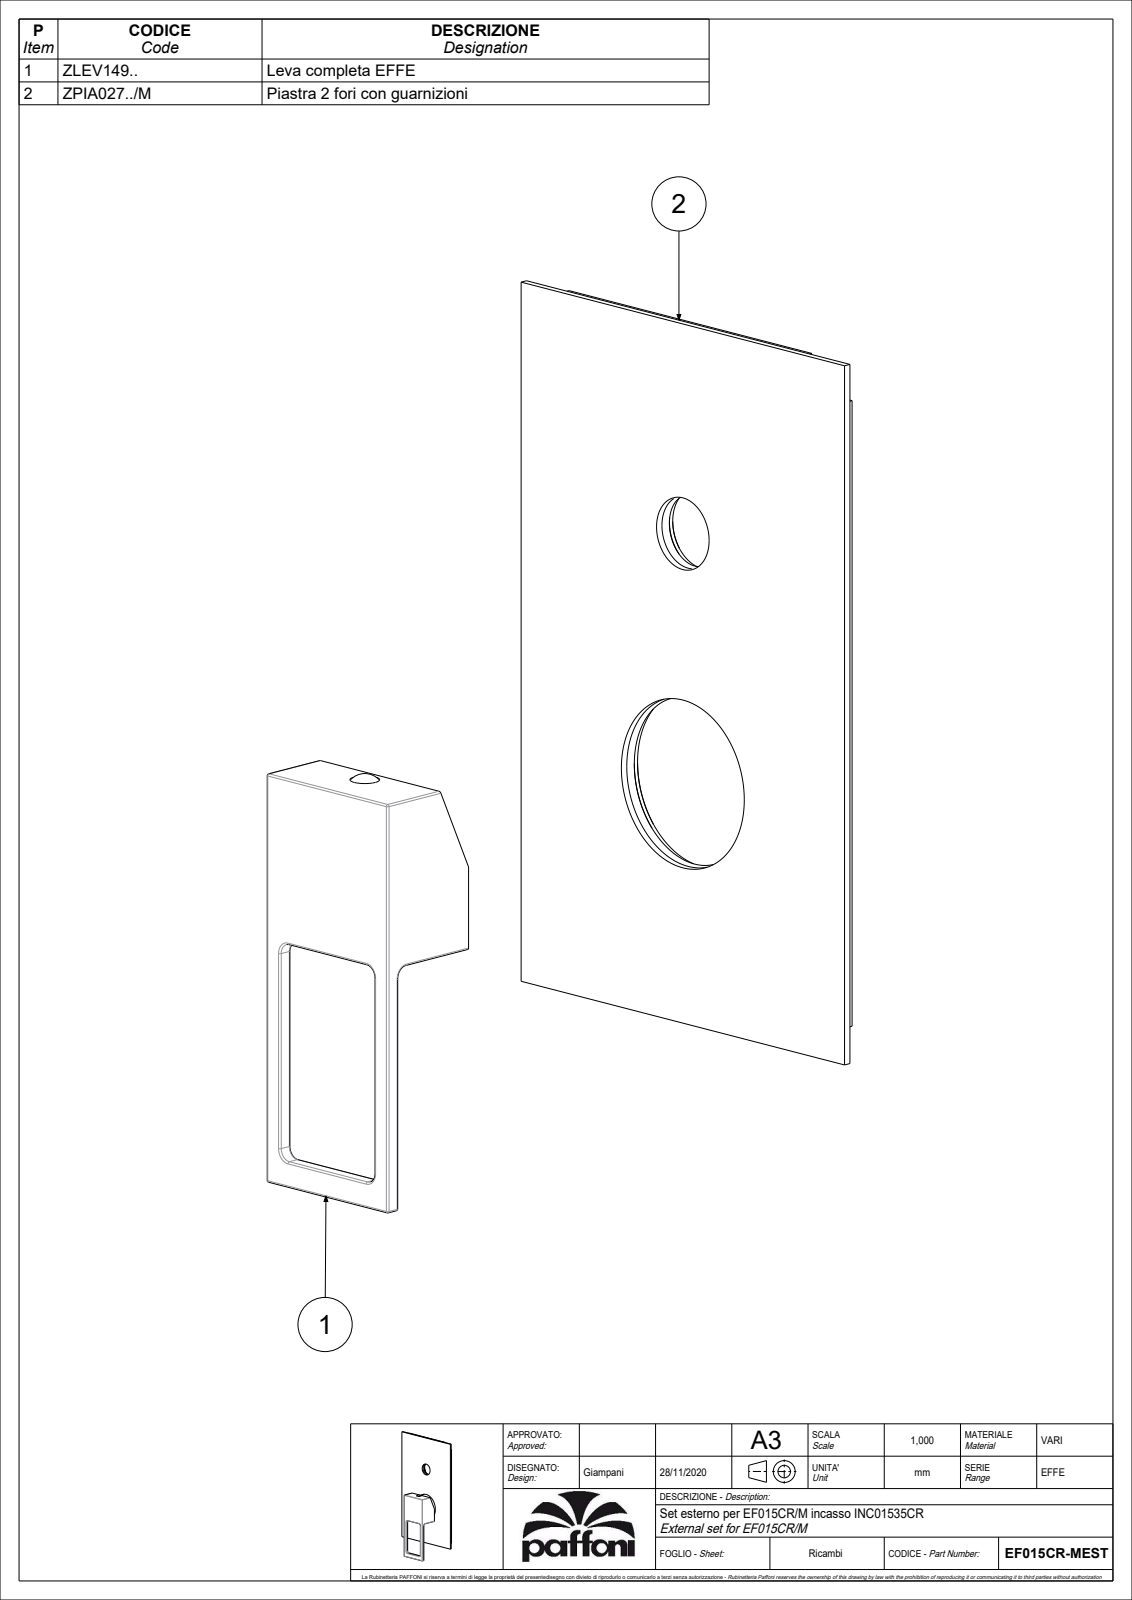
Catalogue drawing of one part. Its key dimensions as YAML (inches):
part_name: "EF015CR-MEST"
step_written_by: "CREO PARAMETRIC BY PTC INC, 2020044 (CONFIG_CONTROL_DESIGN)"
units: inches
bodies: {solids: 2, faces: 182, planar: 81, cylindrical: 67, other: 34}
overall_size: [8.366, 4.724, 1.555]
volume: 4.109
surface_area: 102.4
round_holes:
  - {diameter: 0.118, count: 1}
  - {diameter: 0.177, count: 1}
  - {diameter: 0.217, count: 1}
  - {diameter: 0.307, count: 1}
  - {diameter: 0.768, count: 1}
  - {diameter: 0.846, count: 1}
  - {diameter: 0.984, count: 1}
  - {diameter: 1.795, count: 1}
  - {diameter: 1.874, count: 1}
  - {diameter: 2.012, count: 1}
round_bosses_or_shafts:
  - {diameter: 2.15, count: 1}
  - {diameter: 1.122, count: 1}
  - {diameter: 0.299, count: 1}
  - {diameter: 0.197, count: 1}
partial_cylinders:
  - {radius: 0.02, count: 20}
  - {radius: 0.118, count: 5}
  - {radius: 0.157, count: 1}
face_to_face_distances: [0.079, 0.031, 0.11, 1.37, 1.339, 1.26, 1.772, 0.118, 1.252, 1.22]
hole_center_spacings: [2.677]
